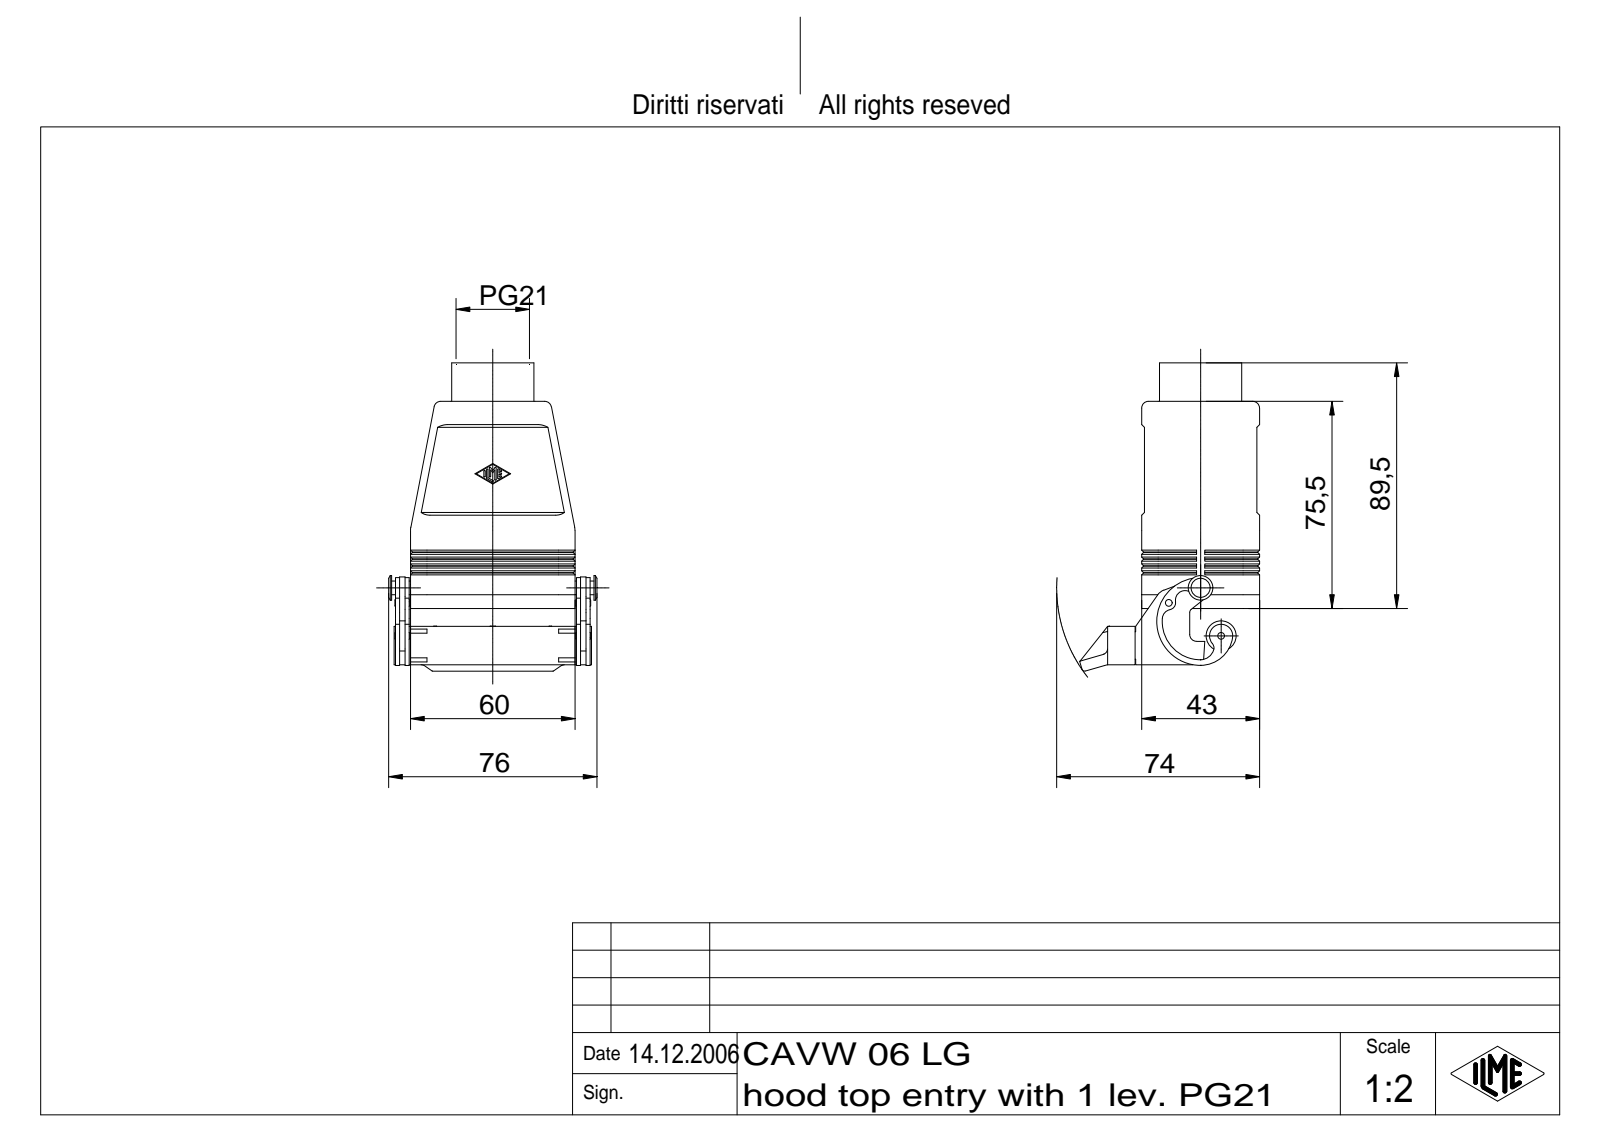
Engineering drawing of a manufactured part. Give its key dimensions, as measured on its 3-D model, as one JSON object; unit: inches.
{"part_name": "CAV Tüllengehäuse 1 Bügel für einen Einsatz", "step_written_by": "Autodesk Inventor 7 (AUTOMOTIVE_DESIGN)", "units": "inches", "bodies": {"solids": 1, "faces": 640, "planar": 236, "cylindrical": 161, "other": 243}, "overall_size": [4.423, 2.992, 2.582], "volume_in3": 4.428, "surface_area_in2": 64.48, "round_holes": [[0.098, 1], [0.976, 1], [1.054, 1]], "round_bosses_or_shafts": [[1.181, 1], [1.015, 1], [0.433, 1], [0.354, 1], [0.197, 1], [0.079, 1]], "partial_cylinders_radius": [[0.01, 14], [0.236, 10], [0.079, 7], [0.098, 7], [0.118, 4], [0.138, 2], [0.197, 2], [0.209, 2]], "face_to_face_distances": [0.157, 1.496, 1.535, 0.039, 0.118, 1.654, 1.378, 0.433, 0.276, 1.693]}
